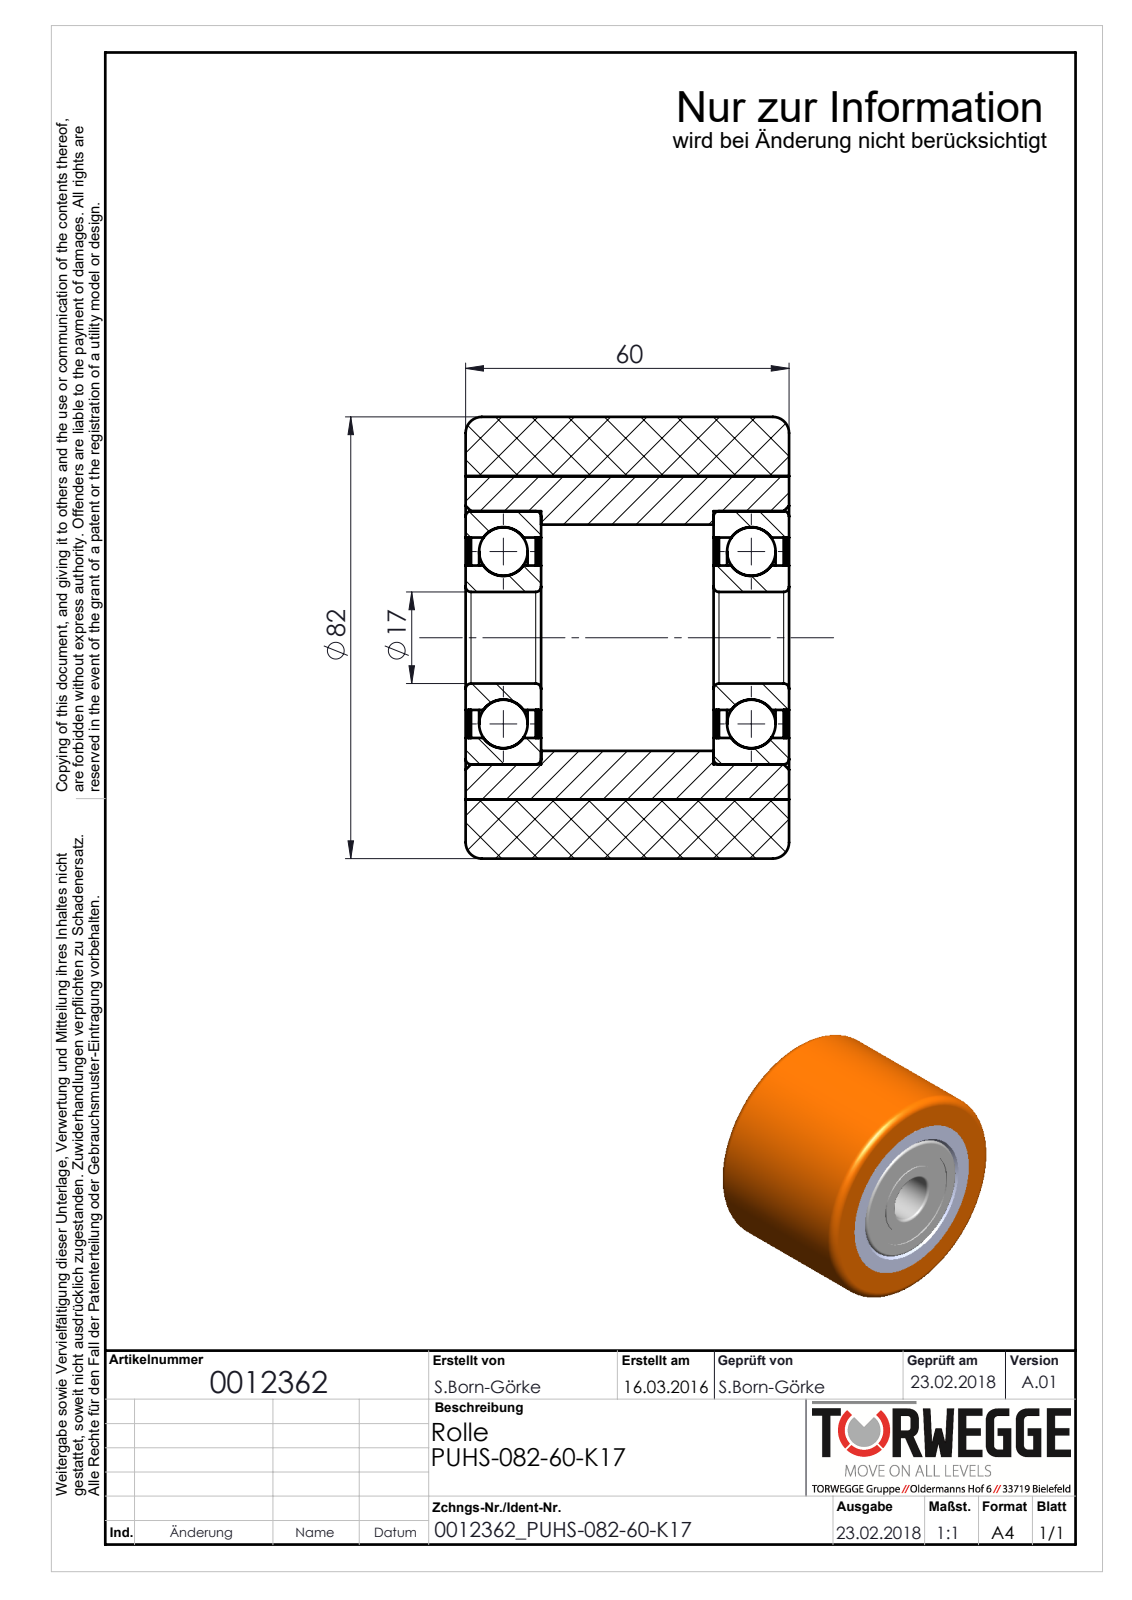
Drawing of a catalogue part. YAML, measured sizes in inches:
part_name: "0012362_PUHS-082-60-K17"
step_written_by: "SolidWorks 2016 (AUTOMOTIVE_DESIGN)"
units: inches
bodies: {solids: 12, faces: 118, planar: 22, cylindrical: 52, other: 44}
overall_size: [3.228, 3.228, 2.362]
volume: 15.85
surface_area: 122.5
round_holes:
  - {diameter: 0.669, count: 1}
  - {diameter: 1.055, count: 1}
  - {diameter: 1.465, count: 1}
  - {diameter: 1.654, count: 1}
  - {diameter: 1.85, count: 1}
  - {diameter: 2.362, count: 1}
round_bosses_or_shafts:
  - {diameter: 3.228, count: 1}
face_to_face_distances: [1.811, 0.02, 2.362, 0.512, 0.551, 0.039, 0.531, 1.831, 0.492, 1.791]
